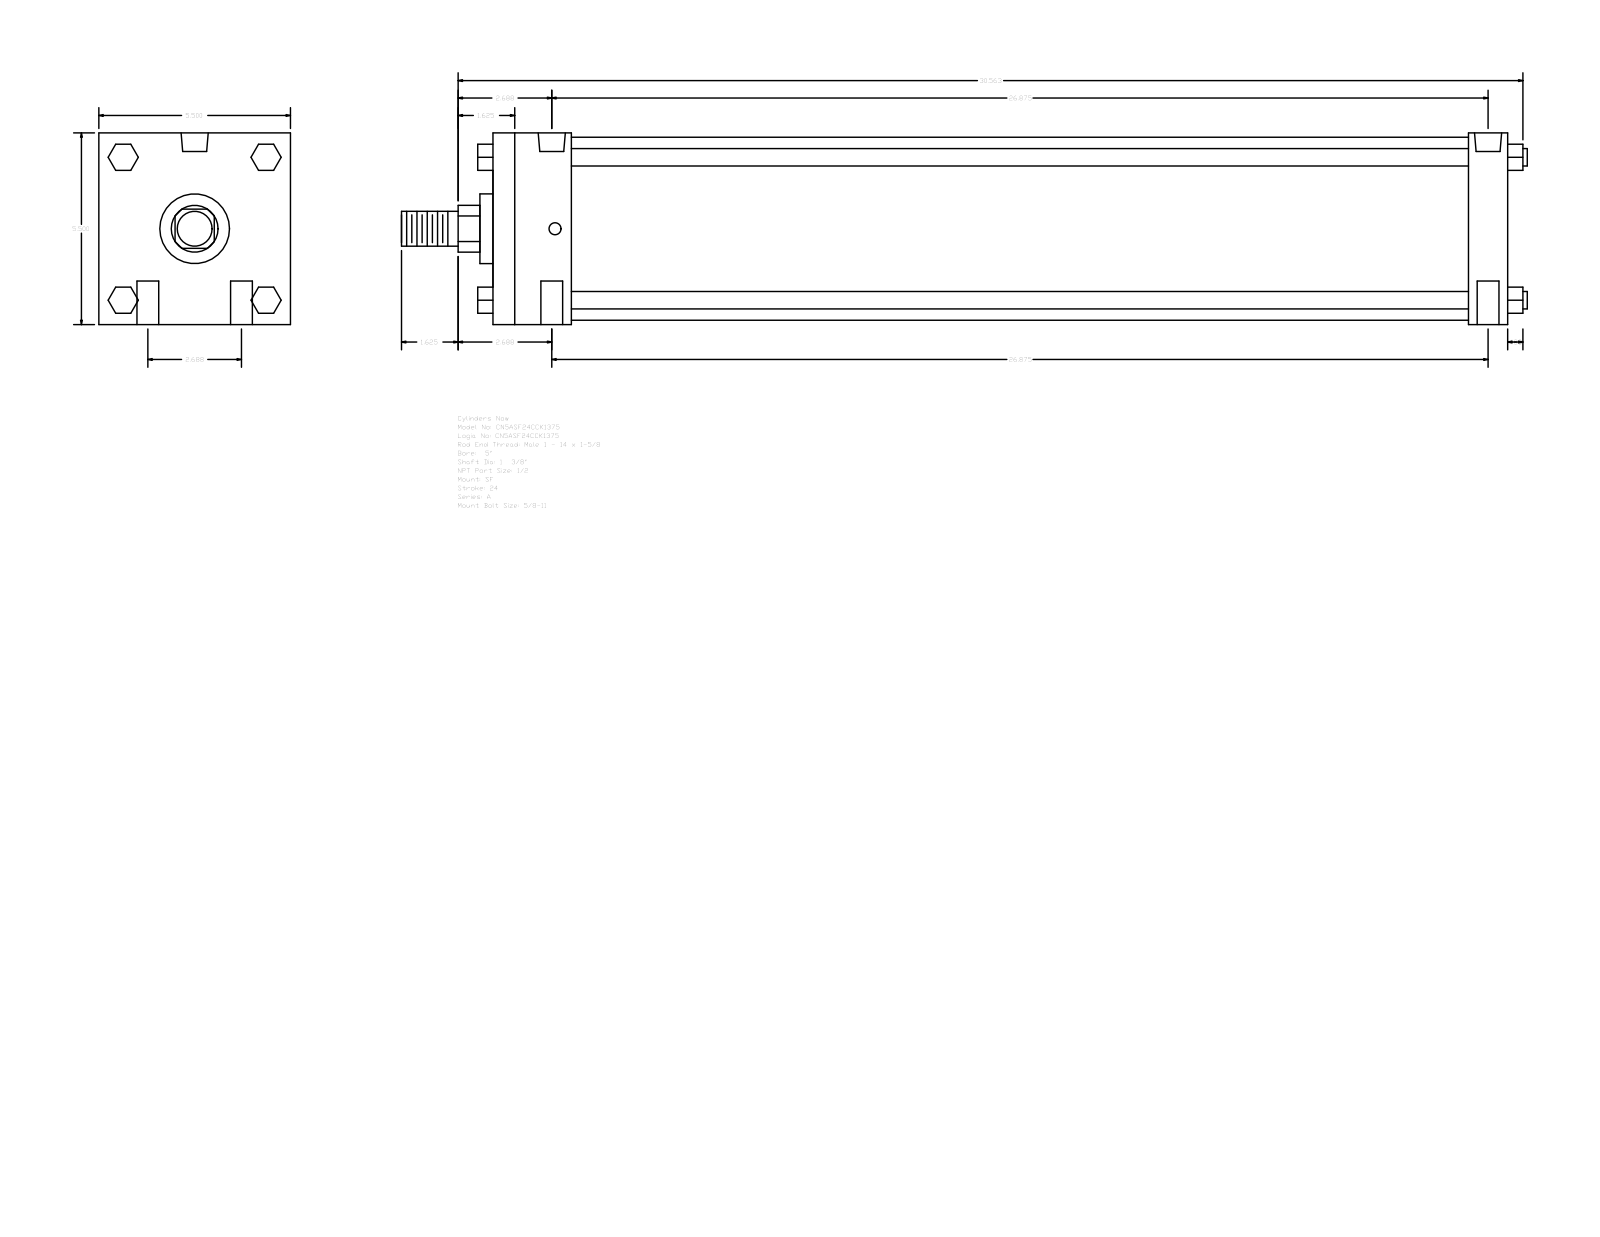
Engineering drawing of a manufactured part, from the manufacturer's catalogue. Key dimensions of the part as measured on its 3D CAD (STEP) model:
Part name (STEP PRODUCT): A_SF__0500_1.375
STEP written by: GSSL Pune (CONFIG_CONTROL_DESIGN)
Units: millimetres
Bodies: 0 solids, 124 faces (94 planar, 30 cylindrical, 0 other)
Overall size (bounding box): 820.74 × 139.7 × 139.7
Round holes (diameter × count): ⌀15.88 ×4, ⌀8.73 ×2, ⌀19.77 ×2
Round bosses / shafts (diameter × count): ⌀12.7 ×4, ⌀133.35 ×1, ⌀50.8 ×1, ⌀34.92 ×1, ⌀25.4 ×1
Partial cylindrical surfaces — rounded edges, fillets, slot ends (radius × count): R17.06 ×1
Main face-to-face distances: 139.7, 739.77, 57.15, 711.2, 654.05, 682.62, 28.57, 19.05, 52.07, 90.18
Hole centre spacings: 34.13, 683.48, 682.63, 68.26, 686.03, 677.85
